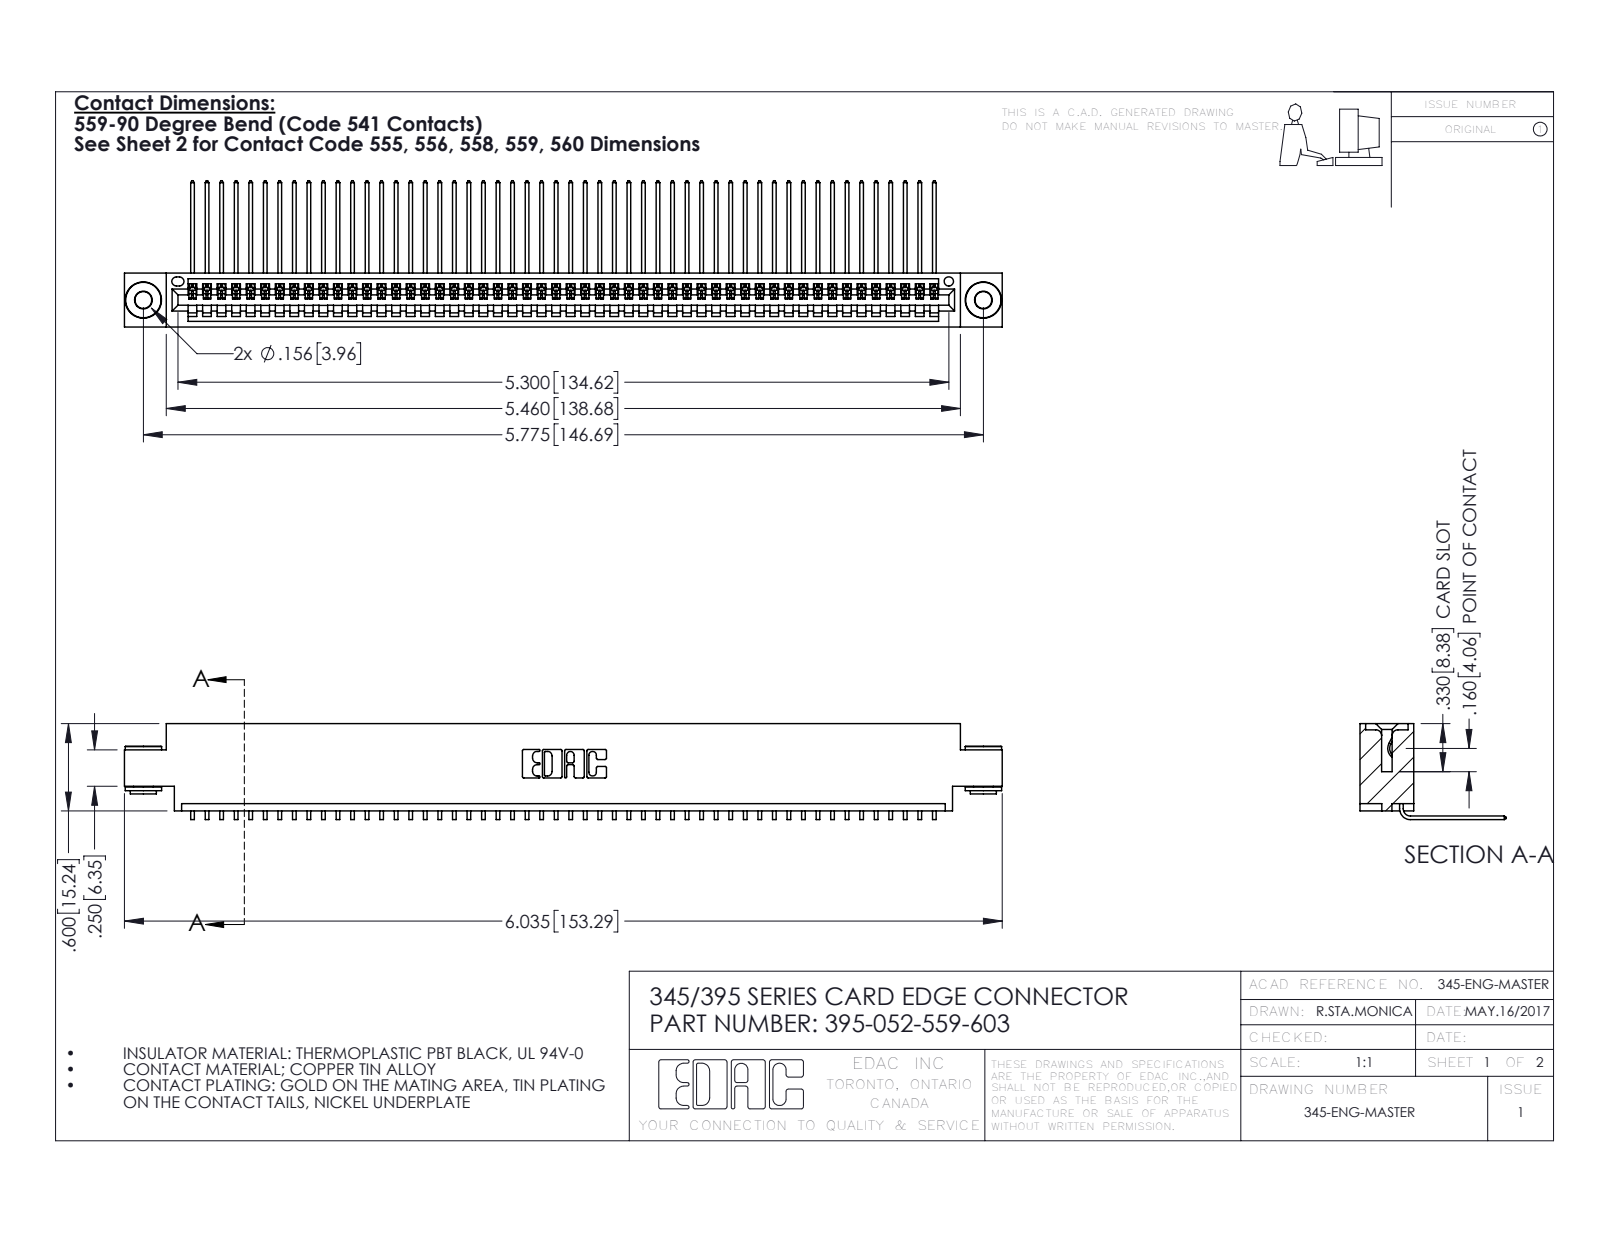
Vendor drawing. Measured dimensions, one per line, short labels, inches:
name: 395-052-559-603; 345-292-001_558 559 Tail - 1; 345-250-002_345-250-002-102; 345 Part_0.170 Offset - 0.156 Dia-TH
written by: SolidWorks 2016 (CONFIG_CONTROL_DESIGN)
unit: in
bodies: 55 solids, 3288 faces (2278 planar, 1002 cylindrical, 8 other)
size: 6.035 × 1.005 × 0.659
volume: 0.898 in³; area: 32.64 in²
holes: 2× ⌀0.116, 2× ⌀0.156, 1× ⌀0.064
bosses: 2× ⌀0.25, 2× ⌀0.18, 2× ⌀0.136
rounds: 104× R0.006, 22× R0.01, 6× R0.007, 6× R0.031, 3× R0.026, 2× R0.031, 2× R0.04, 1× R0.014
face distances: 0.072, 0.298, 0.37, 0.2, 0.098, 0.272, 0.025, 0.225, 0.175, 0.149
hole spacings: 0.27, 5.539, 5.775
